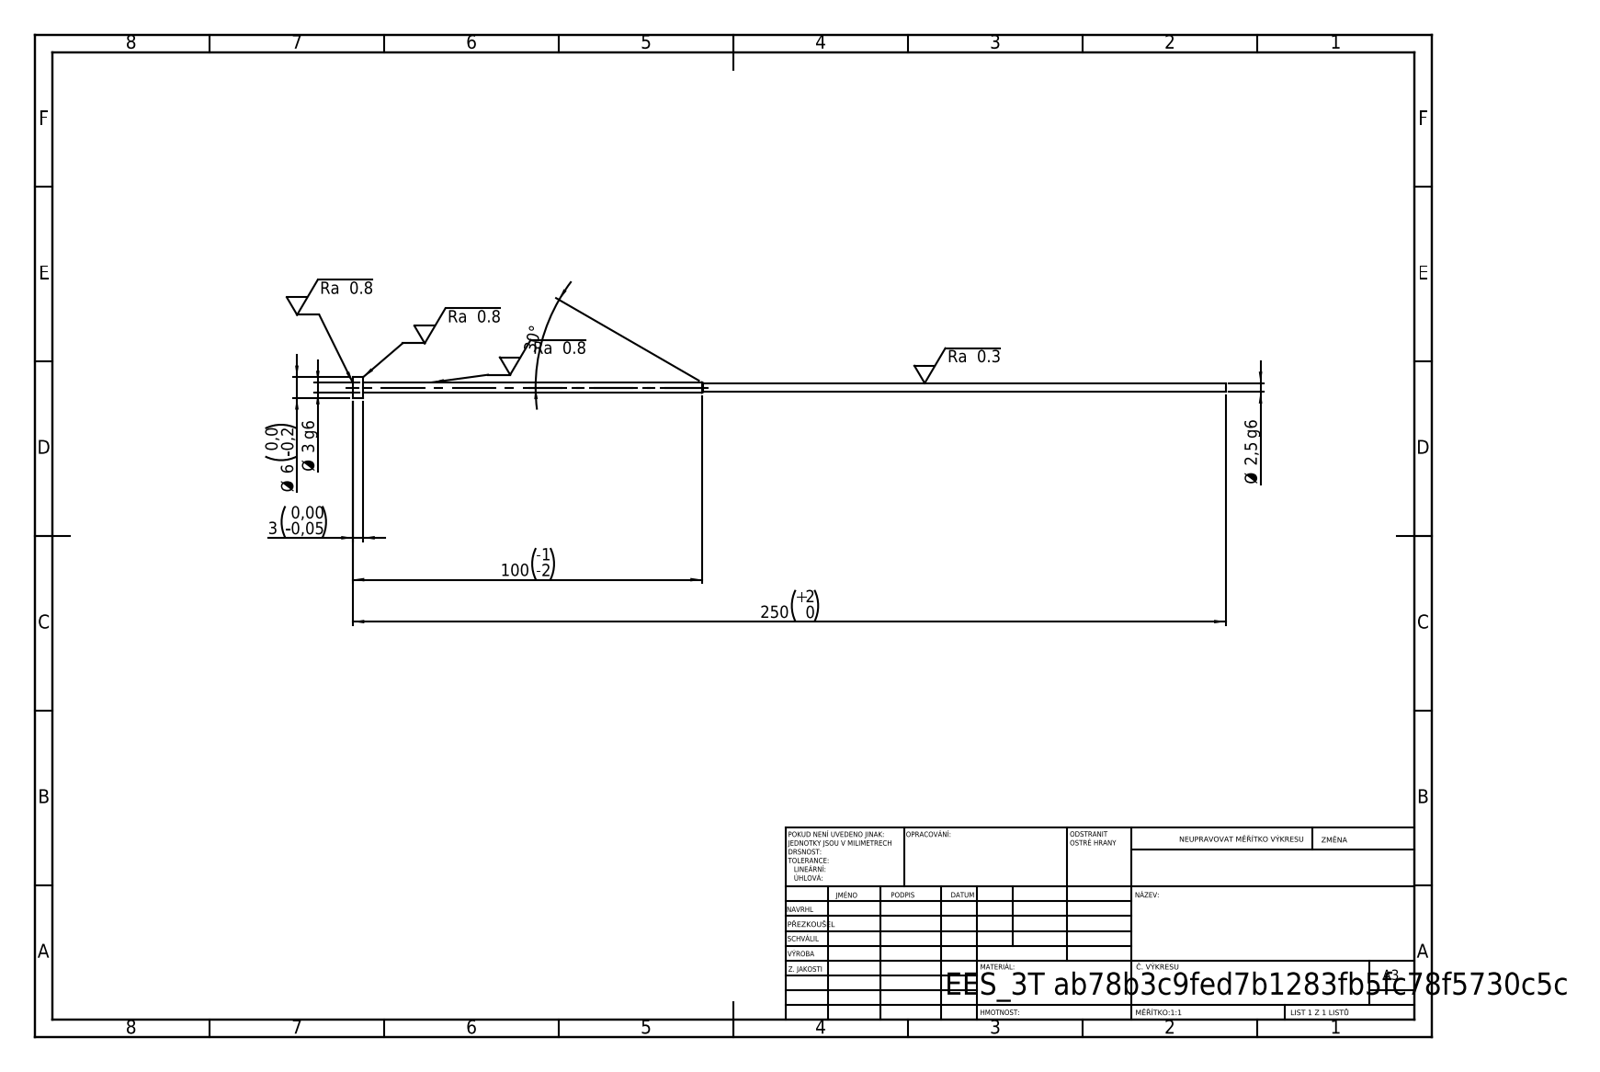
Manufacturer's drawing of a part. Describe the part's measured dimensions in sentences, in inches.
Its 3-D file was written by "SolidWorks 2019 (CONFIG_CONTROL_DESIGN)". It is 1 solid with 11 faces: 3 planar, 6 cylindrical and 2 other. Overall it measures 9.843 by 0.236 by 0.236 inches. Its volume is 0.092 cubic inches and its surface area 3.416 square inches. Round bosses or shafts: 1 of diameter 0.236, 1 of diameter 0.118, 1 of diameter 0.098. The main face-to-face distances are 0.118, 9.724, 9.843.
